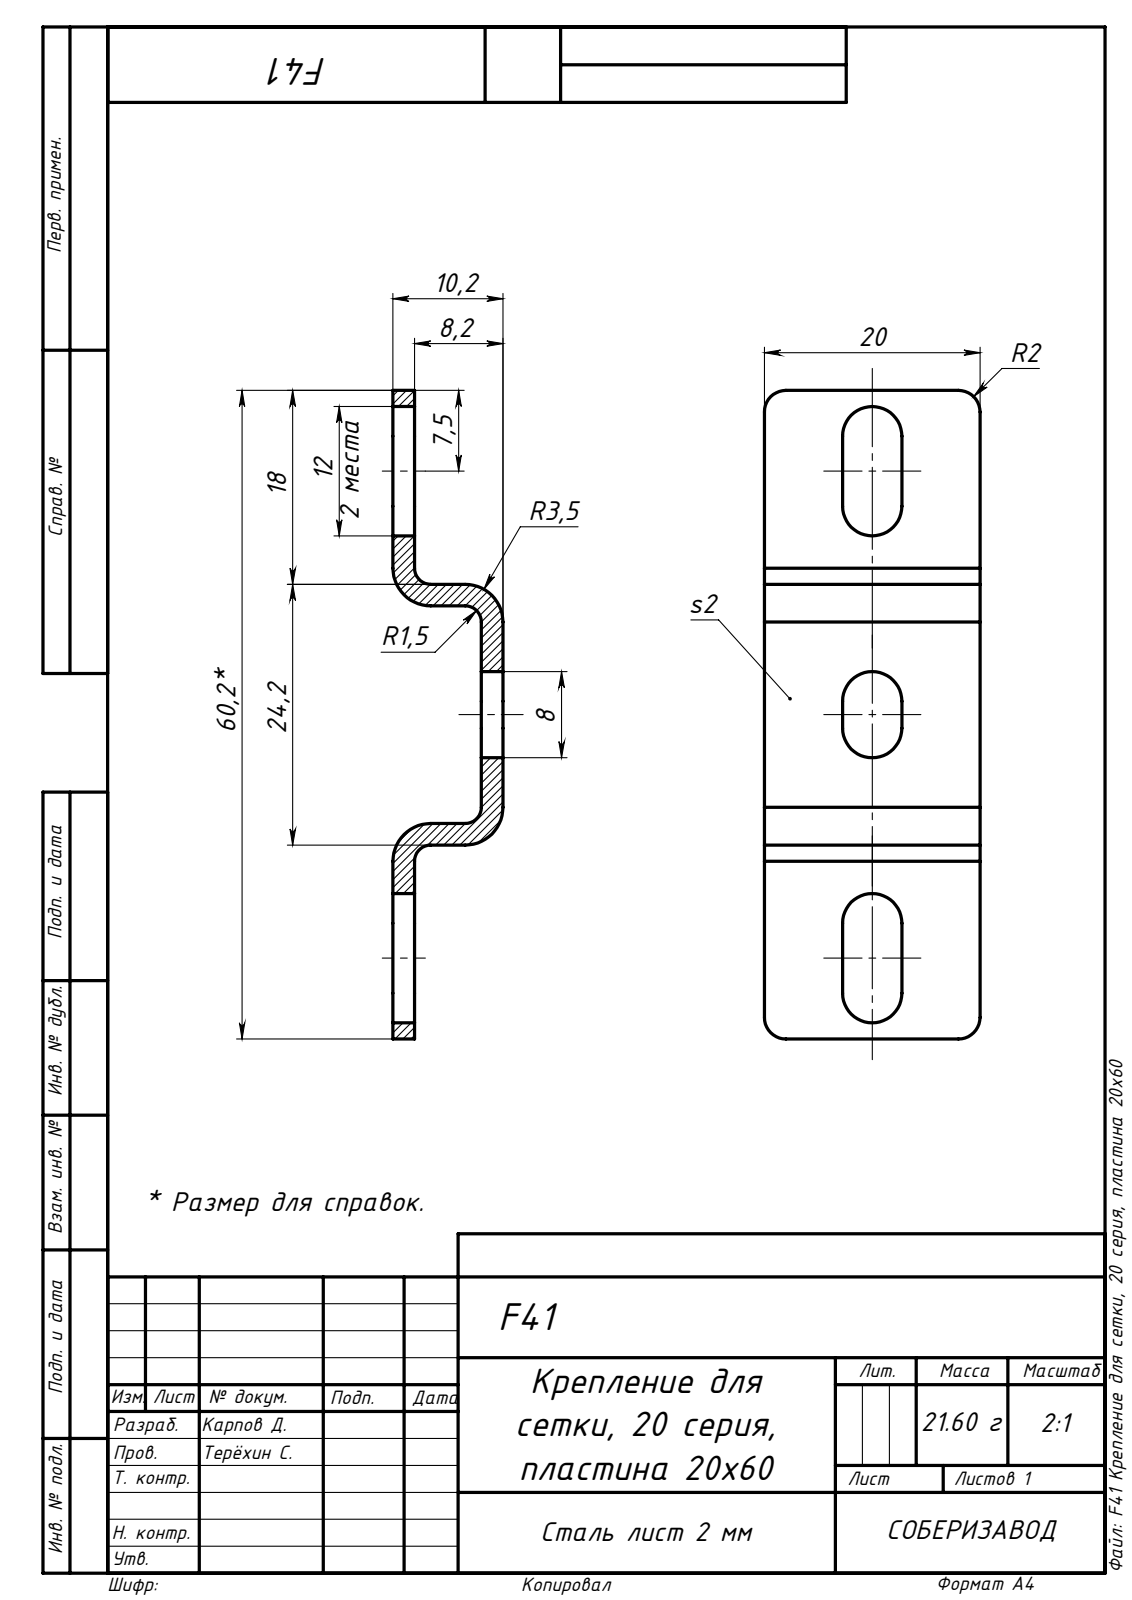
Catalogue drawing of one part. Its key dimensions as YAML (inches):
part_name: "F41 Крепление для сетки, 20 серия, пластина 20х60"
step_written_by: "SolidWorks 2019 (AUTOMOTIVE_DESIGN)"
units: inches
bodies: {solids: 1, faces: 56, planar: 36, cylindrical: 20, other: 0}
overall_size: [2.37, 0.787, 0.402]
volume: 0.157
surface_area: 4.805
partial_cylinders:
  - {radius: 0.108, count: 6}
  - {radius: 0.059, count: 4}
  - {radius: 0.079, count: 4}
  - {radius: 0.138, count: 4}
face_to_face_distances: [0.079, 0.323, 0.402, 0.244, 0.787, 0.874, 0.709, 1.583, 1.661, 0.953]
